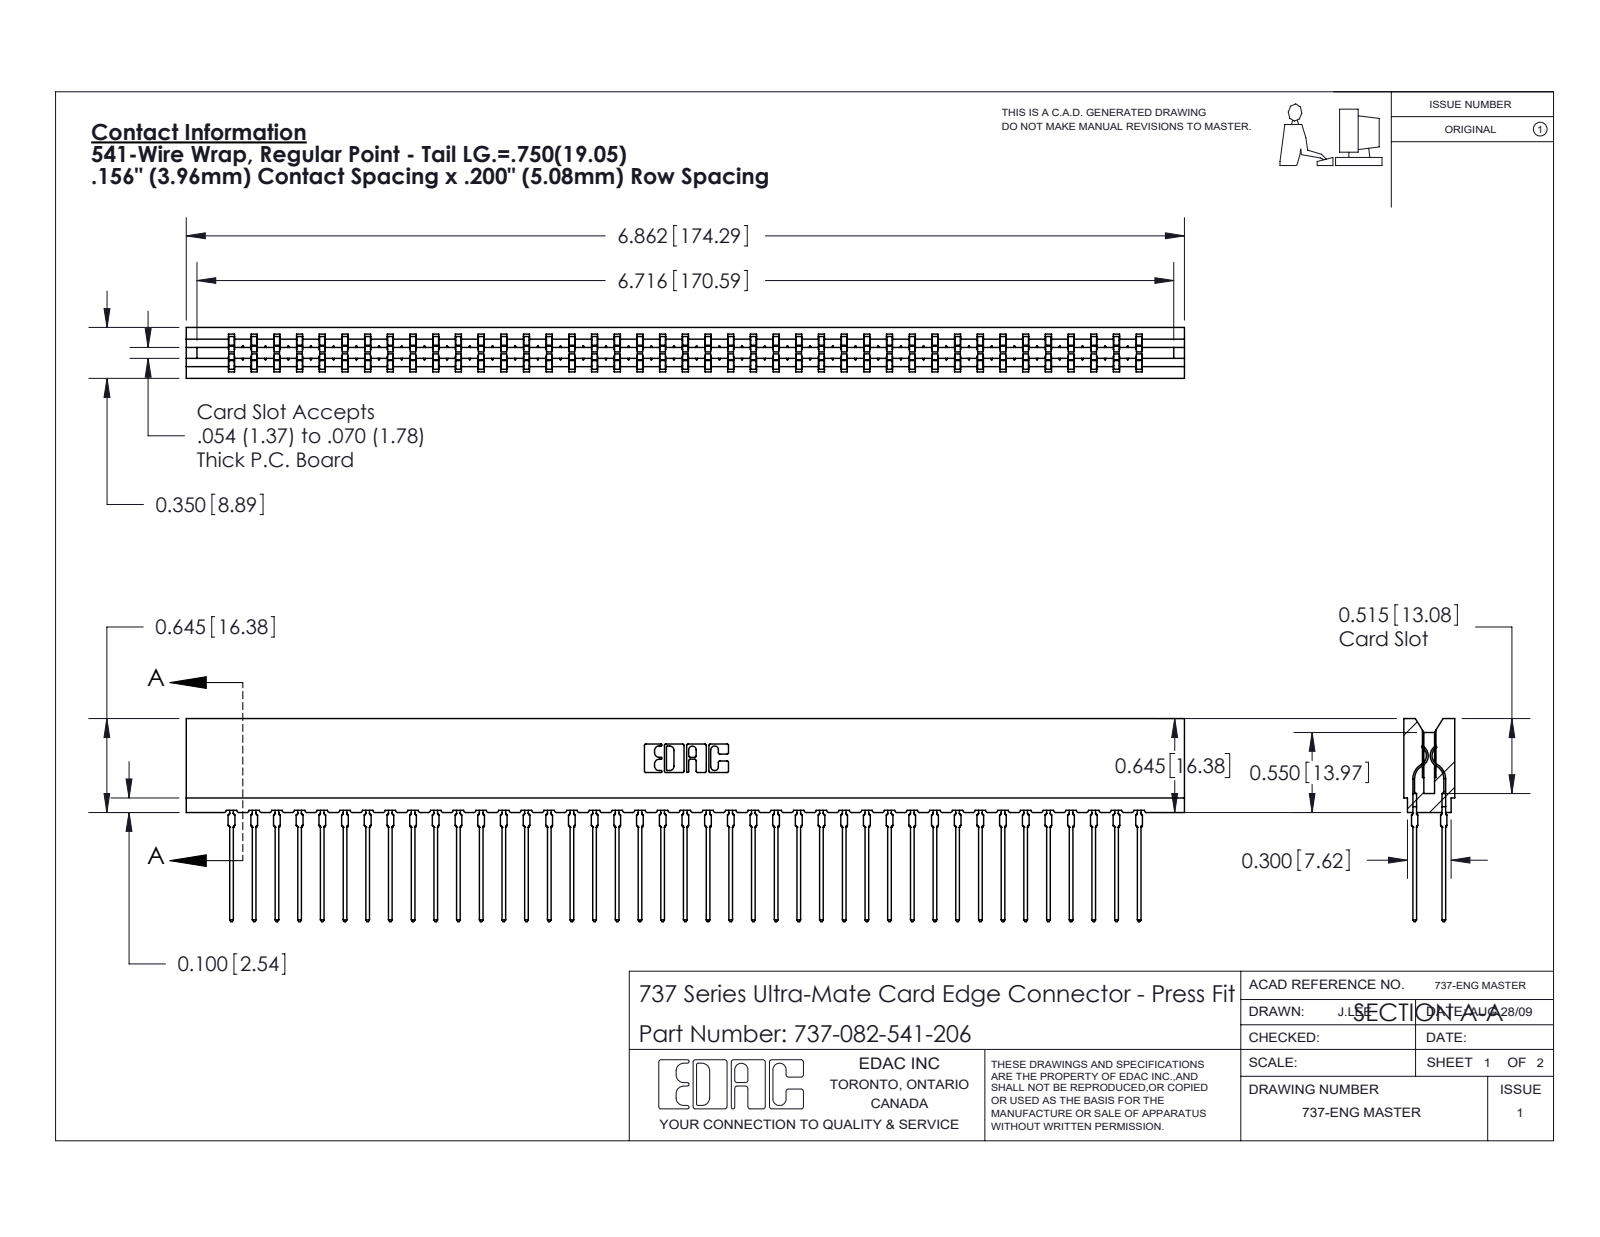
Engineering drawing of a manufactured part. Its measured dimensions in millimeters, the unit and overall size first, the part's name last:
Units: millimetres
Overall size (bounding box): 174.3 × 35.5 × 8.9
Partial cylindrical surfaces — rounded edges, fillets, slot ends (radius × count): R0.5 ×164, R0.4 ×82, R0.3 ×22, R0.1 ×8, R0.3 ×8, R0.2 ×6, R0.8 ×6, R0.7 ×3
Main face-to-face distances: 3.5, 5.4, 8.9, 1.6, 7.3, 1.9, 3.8, 1.9, 5.1, 2.2
Volume: 17 620 mm³ · Surface area: 27 440 mm²
Bodies: 83 solids, 7475 faces (3868 planar, 1475 cylindrical, 2132 other)
Part name (STEP PRODUCT): 737 Part_Insulator Option - 06; 745-292-001_541; 737-082-541-206
STEP written by: SolidWorks 2020 (CONFIG_CONTROL_DESIGN)
